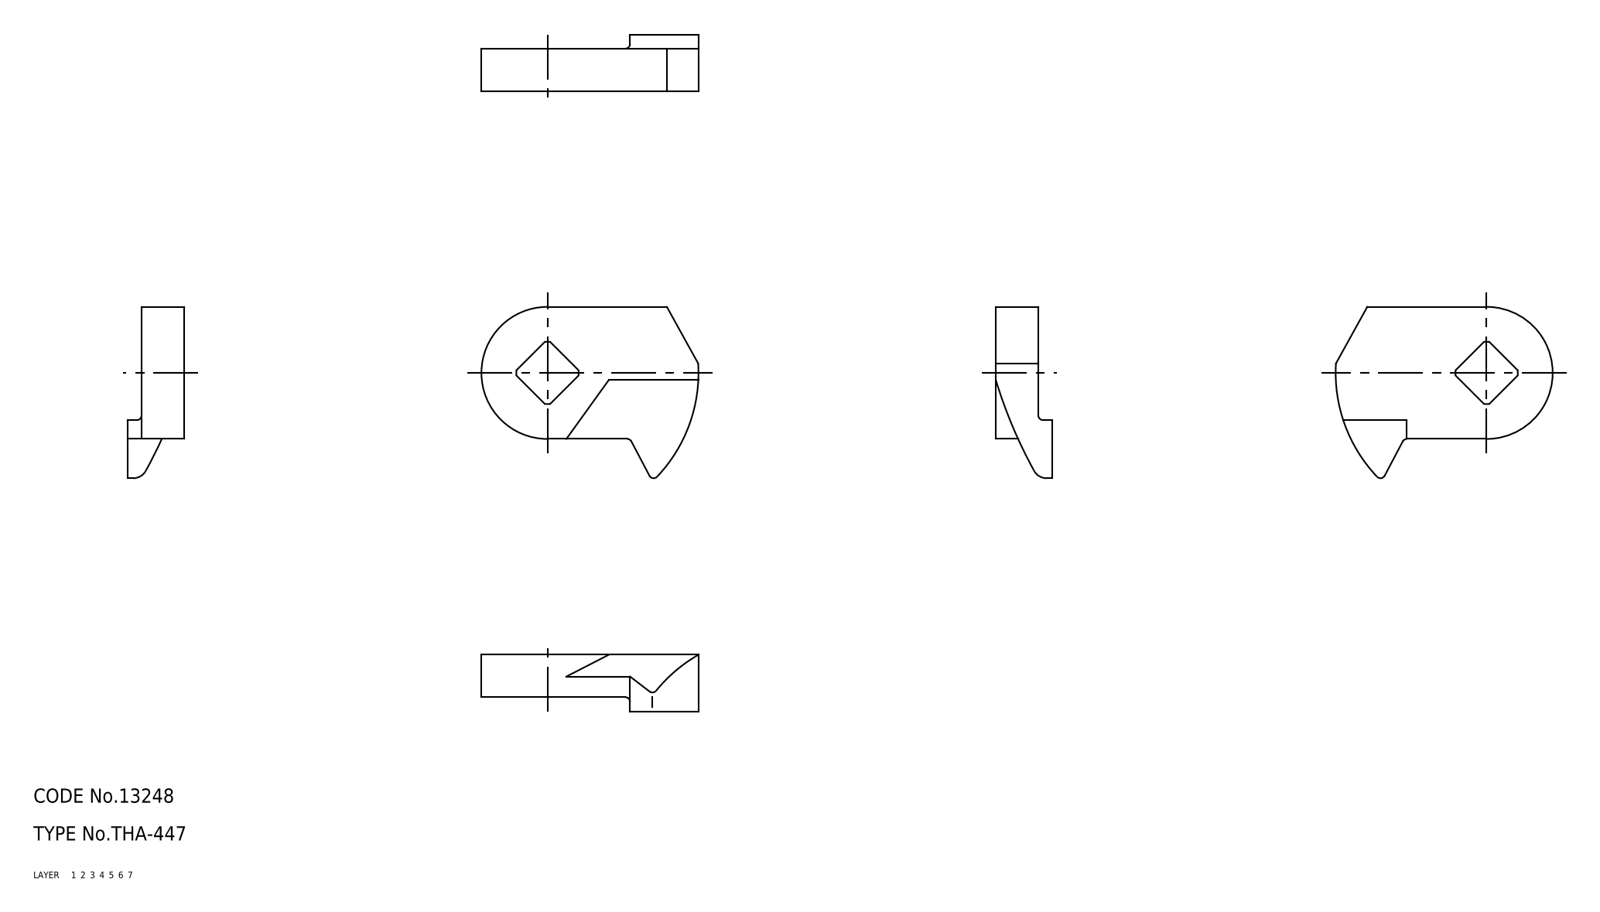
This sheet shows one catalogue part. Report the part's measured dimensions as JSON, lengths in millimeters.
{"part_name": "cam", "step_written_by": "CADfix (AUTOMOTIVE_DESIGN)", "units": "millimeters", "bodies": {"solids": 1, "faces": 27, "planar": 0, "cylindrical": 0, "other": 27}, "overall_size": [46, 36.33, 12], "volume_mm3": 9253, "surface_area_mm2": 3739}
